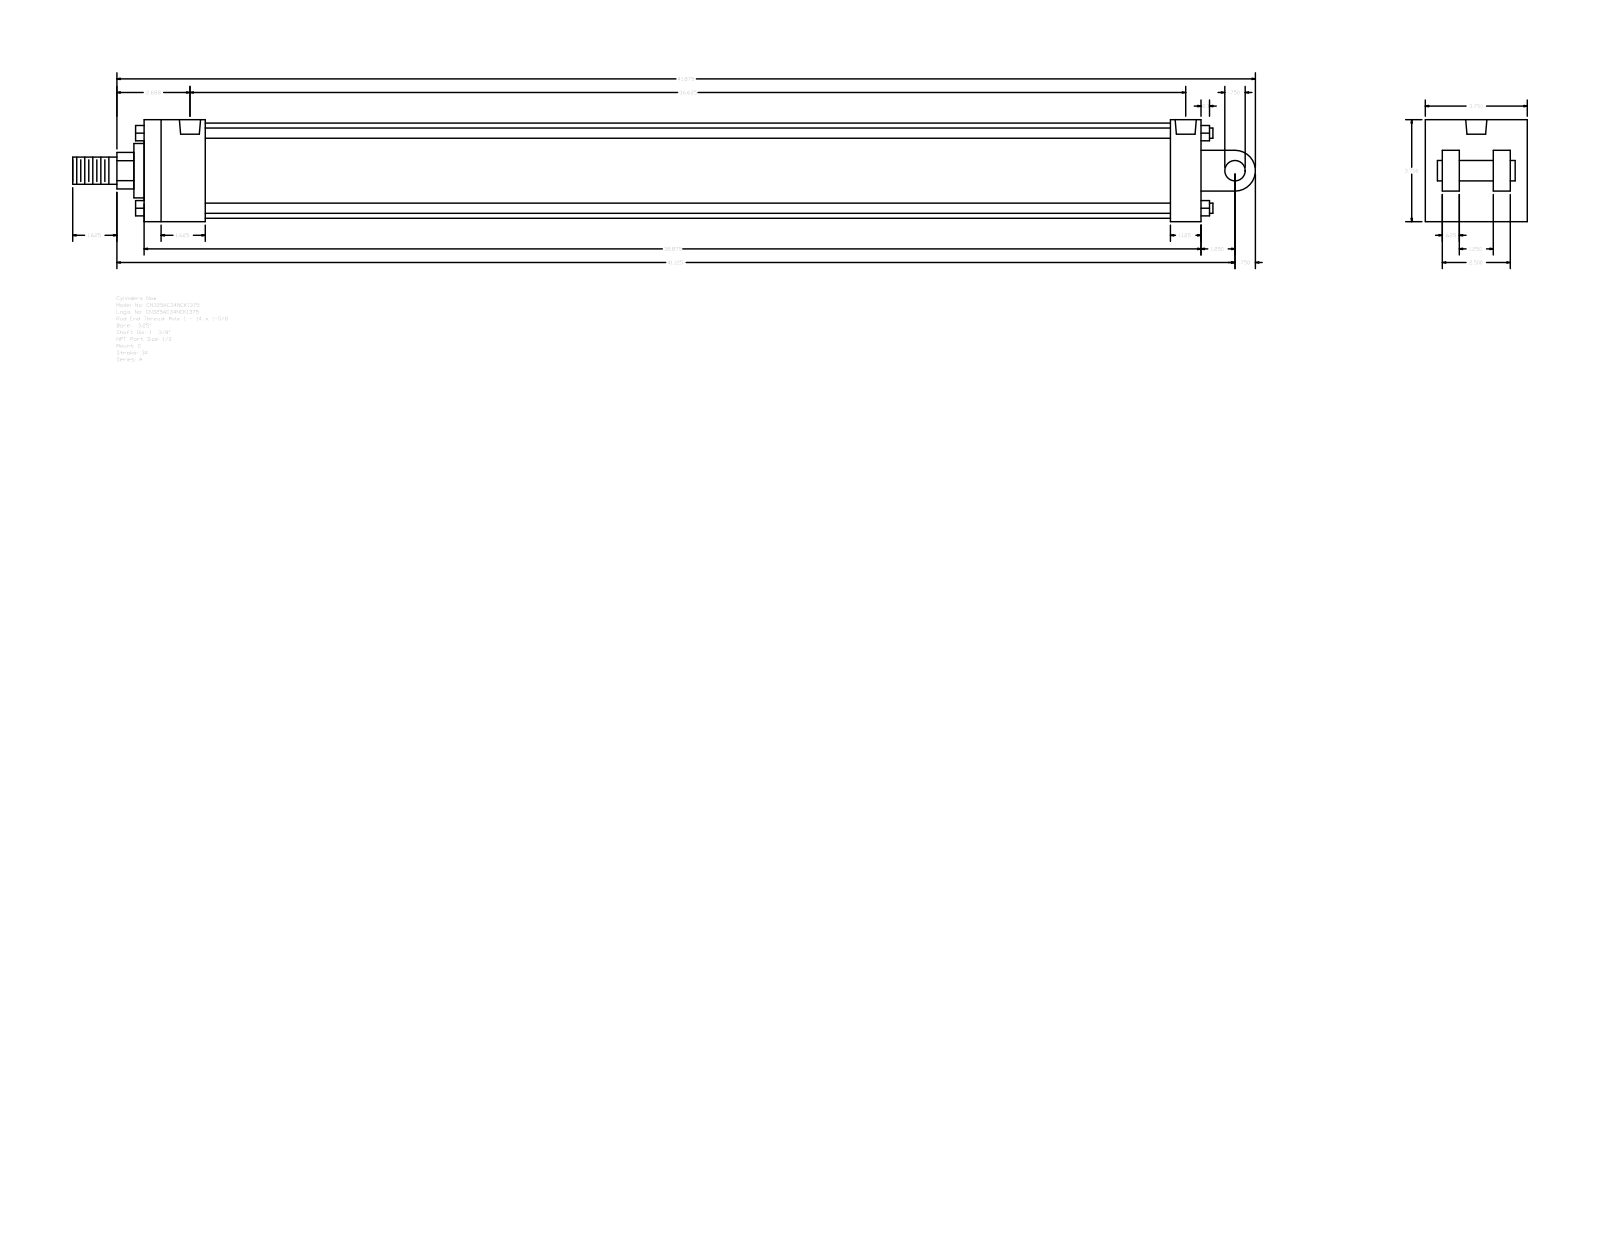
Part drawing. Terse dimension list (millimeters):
name: A_C__0325_1.375
written by: GSSL Pune (CONFIG_CONTROL_DESIGN)
unit: mm
bodies: 0 solids, 135 faces (102 planar, 33 cylindrical, 0 other)
size: 1104.9 × 95.25 × 95.25
holes: 4× ⌀8.73, 2× ⌀19.77
bosses: 4× ⌀9.53, 1× ⌀88.9, 1× ⌀50.8, 1× ⌀34.92, 1× ⌀25.4, 1× ⌀19.05
rounds: 1× R17.06, 1× R19.05
face distances: 95.24, 987.43, 15.87, 63.5, 66.67, 57.15, 28.58, 31.74, 79.37, 47.63
hole spacings: 3.18, 923.92, 927.1, 930.28
